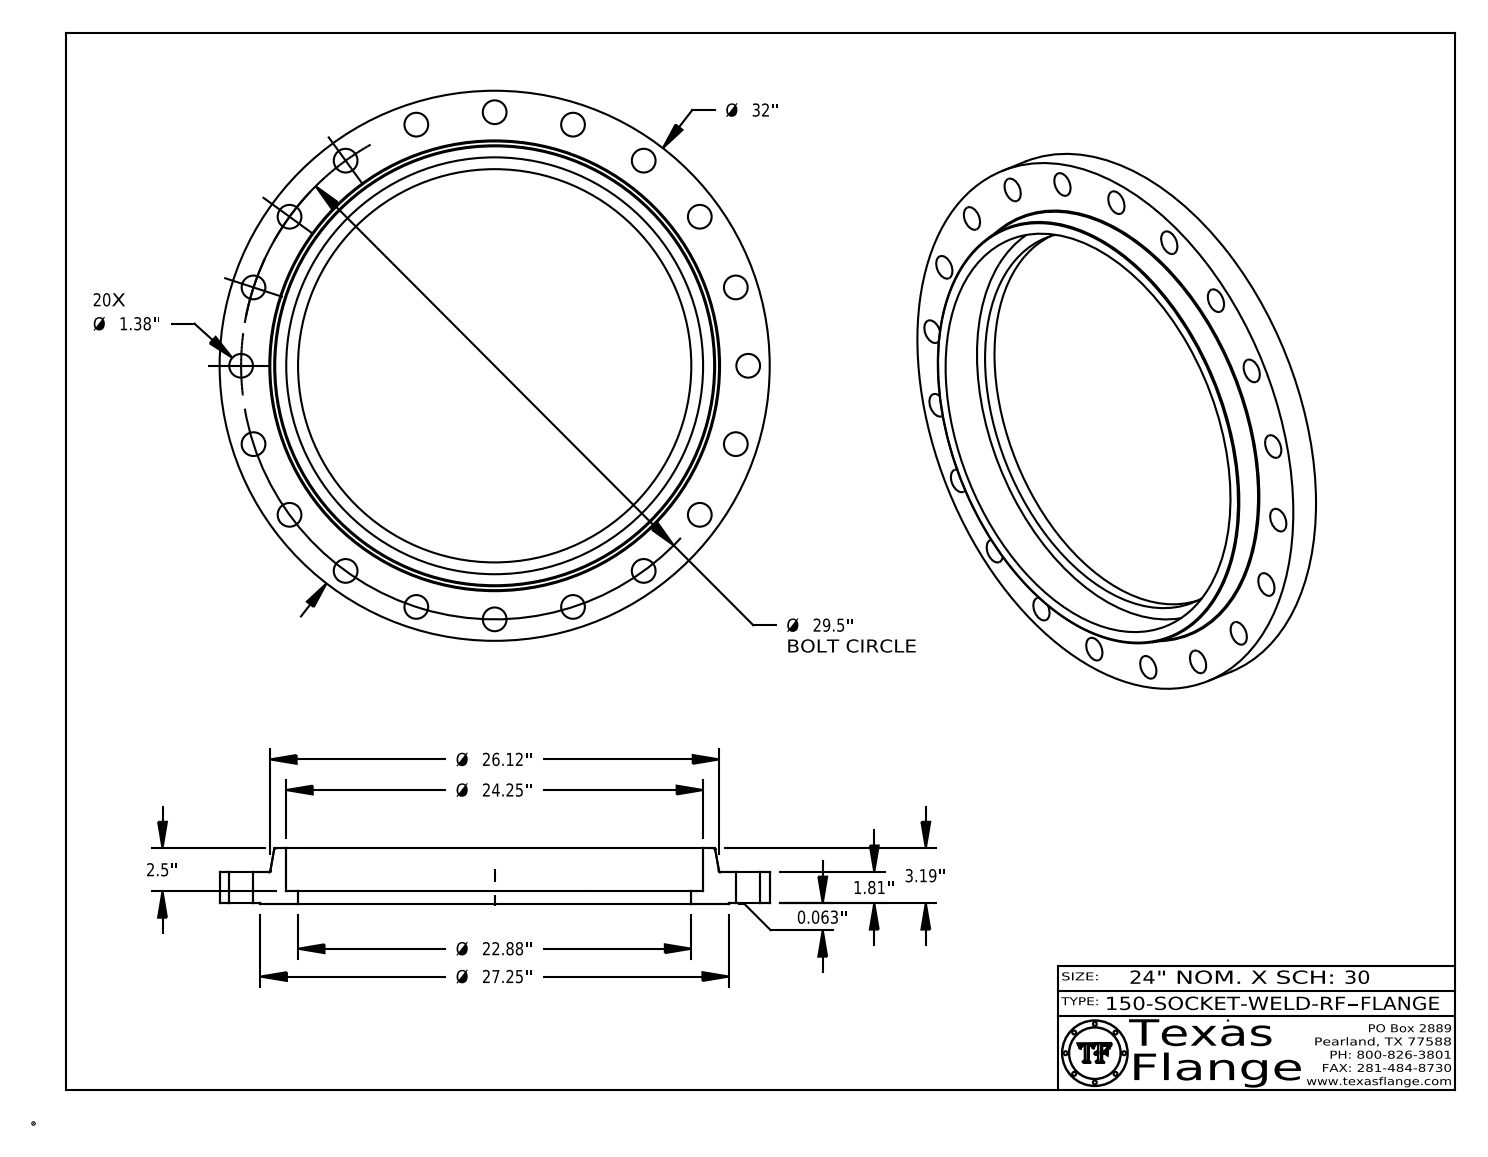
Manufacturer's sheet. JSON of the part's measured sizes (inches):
{"part_name": "150-SOCKET-WELD-RF", "step_written_by": "CATIA V5 STEP AP214 (AUTOMOTIVE_DESIGN)", "units": "inches", "bodies": {"solids": 1, "faces": 444, "planar": 370, "cylindrical": 68, "other": 6}, "overall_size": [32, 32, 3.253], "volume_in3": 699.8, "surface_area_in2": 1407, "round_holes": [[1.38, 20], [0.495, 1], [22.876, 1], [24.25, 1]], "round_bosses_or_shafts": [[0.03, 8], [32, 1], [27.25, 1], [0.39, 1]], "face_to_face_distances": [1.81, 0.063, 1.872, 0.753, 0.69, 1.12, 3.253, 3.19, 2.5, 1.38], "hole_center_spacings": [14.75, 29.137, 4.615, 17.34, 20.859, 23.866, 26.285, 9.116]}
